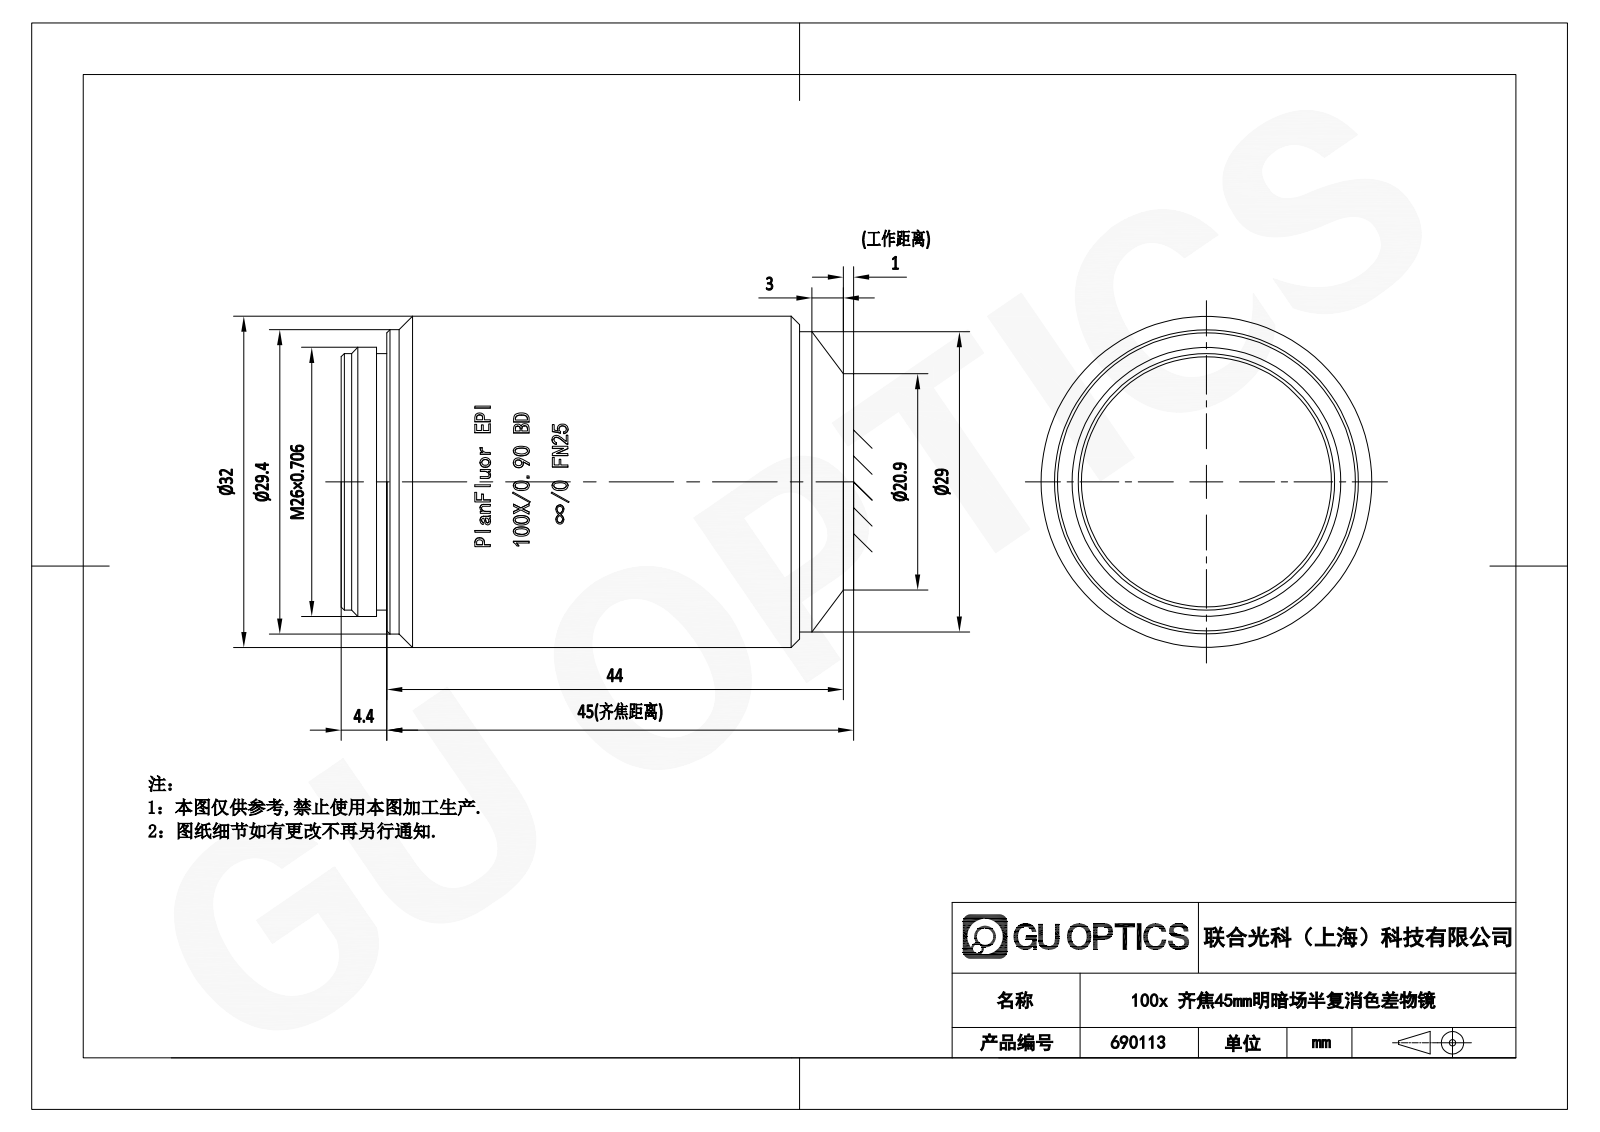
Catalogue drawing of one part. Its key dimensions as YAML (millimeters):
part_name: "690113"
step_written_by: "SolidWorks 2020 (CONFIG_CONTROL_DESIGN)"
units: millimeters
bodies: {solids: 1, faces: 340, planar: 141, cylindrical: 57, other: 142}
overall_size: [48.54, 32.05, 32]
volume: 36333
surface_area: 6068
round_bosses_or_shafts:
  - {diameter: 32, count: 1}
  - {diameter: 29.4, count: 1}
  - {diameter: 29, count: 1}
  - {diameter: 26, count: 1}
  - {diameter: 24.8, count: 1}
partial_cylinders:
  - {radius: 16.05, count: 1}
face_to_face_distances: [48.54, 4.4, 44.14, 44.3, 39.9, 4.24, 3.4, 1, 40.9, 45.14]
